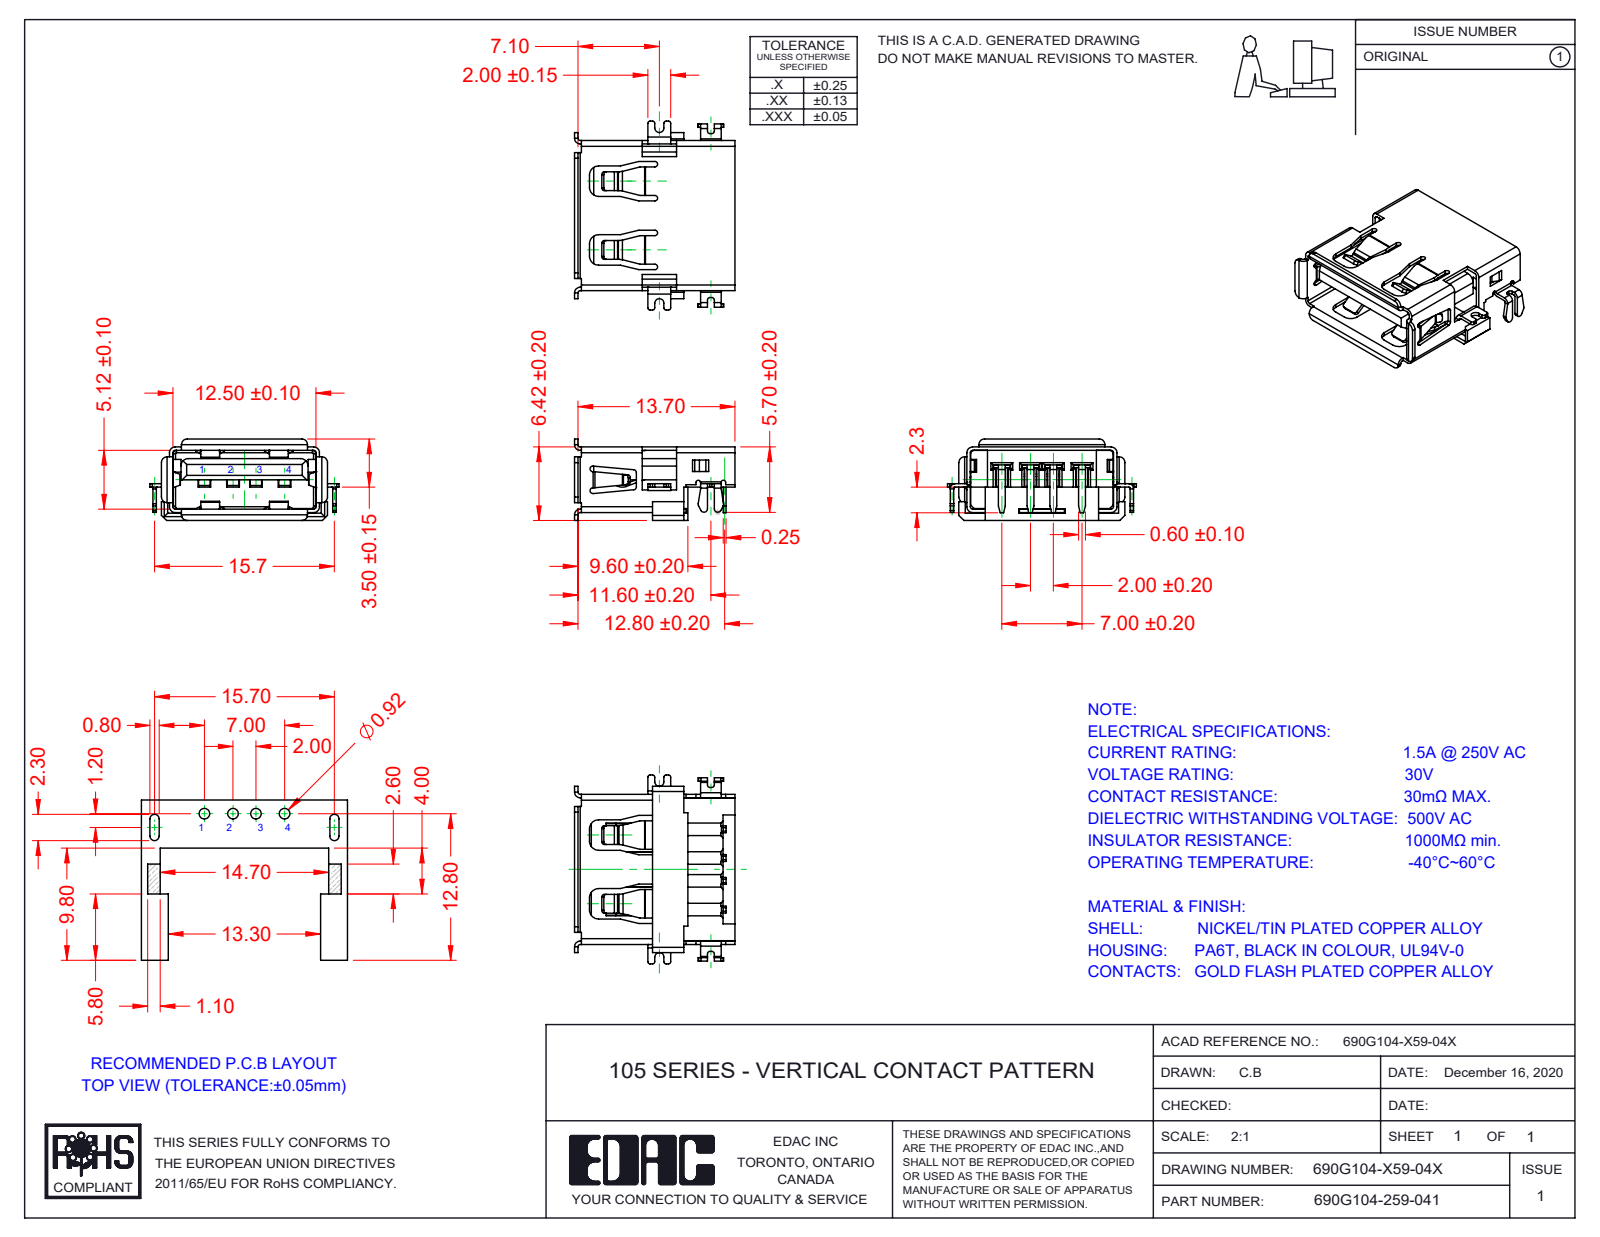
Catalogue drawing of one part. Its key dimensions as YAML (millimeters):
part_name: "Shell 690G104-X59-04X; 690G104-159-041; Contacts 690G104-X59-04X; Insulator 690G104-X59-04X_Black"
step_written_by: "SolidWorks 2020 (AUTOMOTIVE_DESIGN)"
units: millimeters
bodies: {solids: 6, faces: 831, planar: 604, cylindrical: 201, other: 26}
overall_size: [16.5, 14, 7.12]
volume: 424
surface_area: 1771
partial_cylinders:
  - {radius: 0.2, count: 34}
  - {radius: 0.5, count: 24}
  - {radius: 0.25, count: 21}
  - {radius: 0.1, count: 12}
  - {radius: 0.3, count: 8}
  - {radius: 0.4, count: 7}
  - {radius: 0.8, count: 6}
  - {radius: 0.15, count: 3}
face_to_face_distances: [5.42, 2.56, 2.86, 0.72, 4.7, 2.5, 1, 1.02, 5.12, 0.7]
